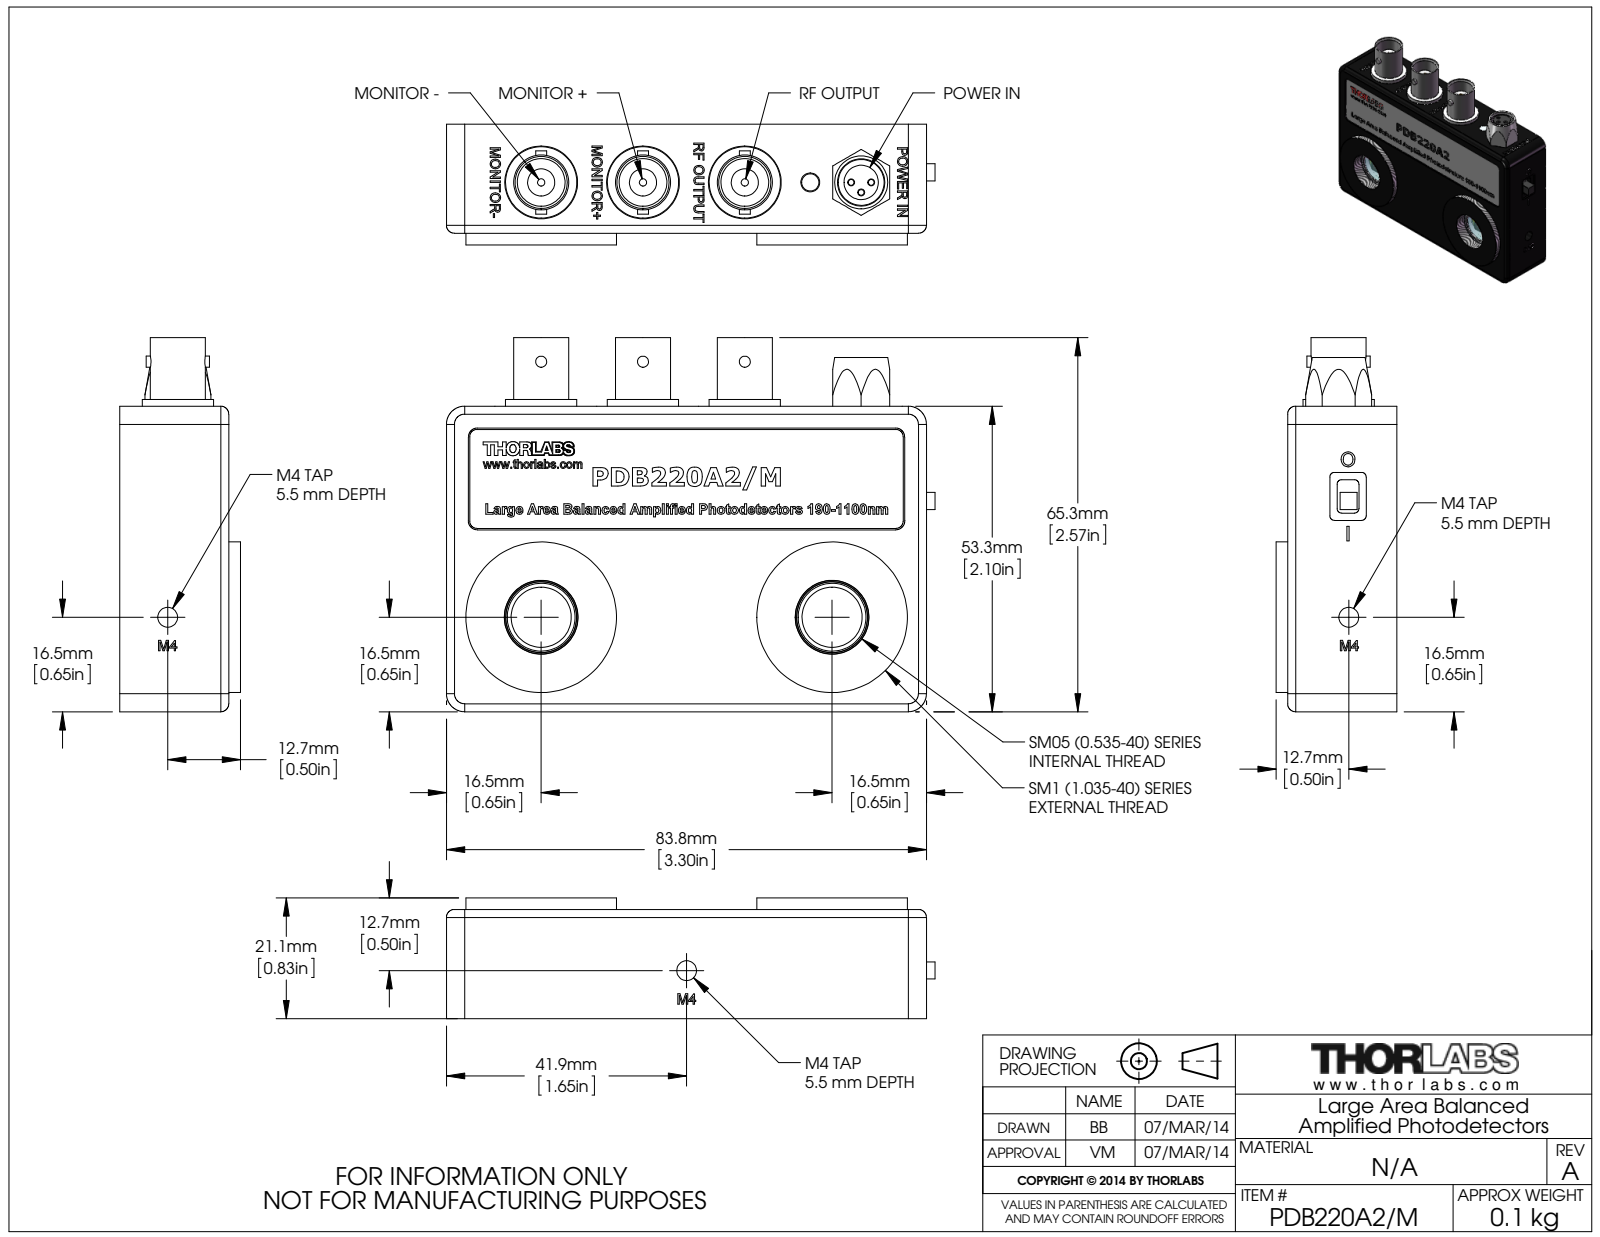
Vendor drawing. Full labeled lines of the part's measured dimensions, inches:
Part name (STEP PRODUCT): MTN003814-E0W
STEP written by: SolidWorks 2013 (AUTOMOTIVE_DESIGN)
Units: inches
Bodies: 37 solids, 2839 faces (1724 planar, 318 cylindrical, 797 other)
Overall size (bounding box): 3.357 × 2.571 × 0.83
Volume: 2.028 in³ · Surface area: 59.81 in²
Round holes (diameter × count): ⌀0.063 ×7, ⌀0.094 ×4, ⌀0.125 ×4, ⌀0.039 ×3, ⌀0.05 ×3, ⌀0.052 ×3, ⌀0.328 ×3, ⌀0.438 ×3, ⌀0.5 ×3, ⌀0.136 ×2, ⌀0.413 ×2, ⌀0.467 ×2
Round bosses / shafts (diameter × count): ⌀0.02 ×6, ⌀0.118 ×5, ⌀0.49 ×3, ⌀0.43 ×3, ⌀0.378 ×3, ⌀0.37 ×3, ⌀0.323 ×3, ⌀0.21 ×3
Partial cylindrical surfaces — rounded edges, fillets, slot ends (radius × count): R0.125 ×31, R0.13 ×14, R0.031 ×8, R0.095 ×8, R0.05 ×4, R0.055 ×4, R0.063 ×4, R0.11 ×4
Main face-to-face distances: 0.063, 0.1, 0.05, 0.68, 0.617, 0.73, 0.667, 0.07, 0.02, 0.75
Hole centre spacings: 0.069, 0.097, 0.599, 0.7, 0.883, 0.893, 1.031, 1.377
